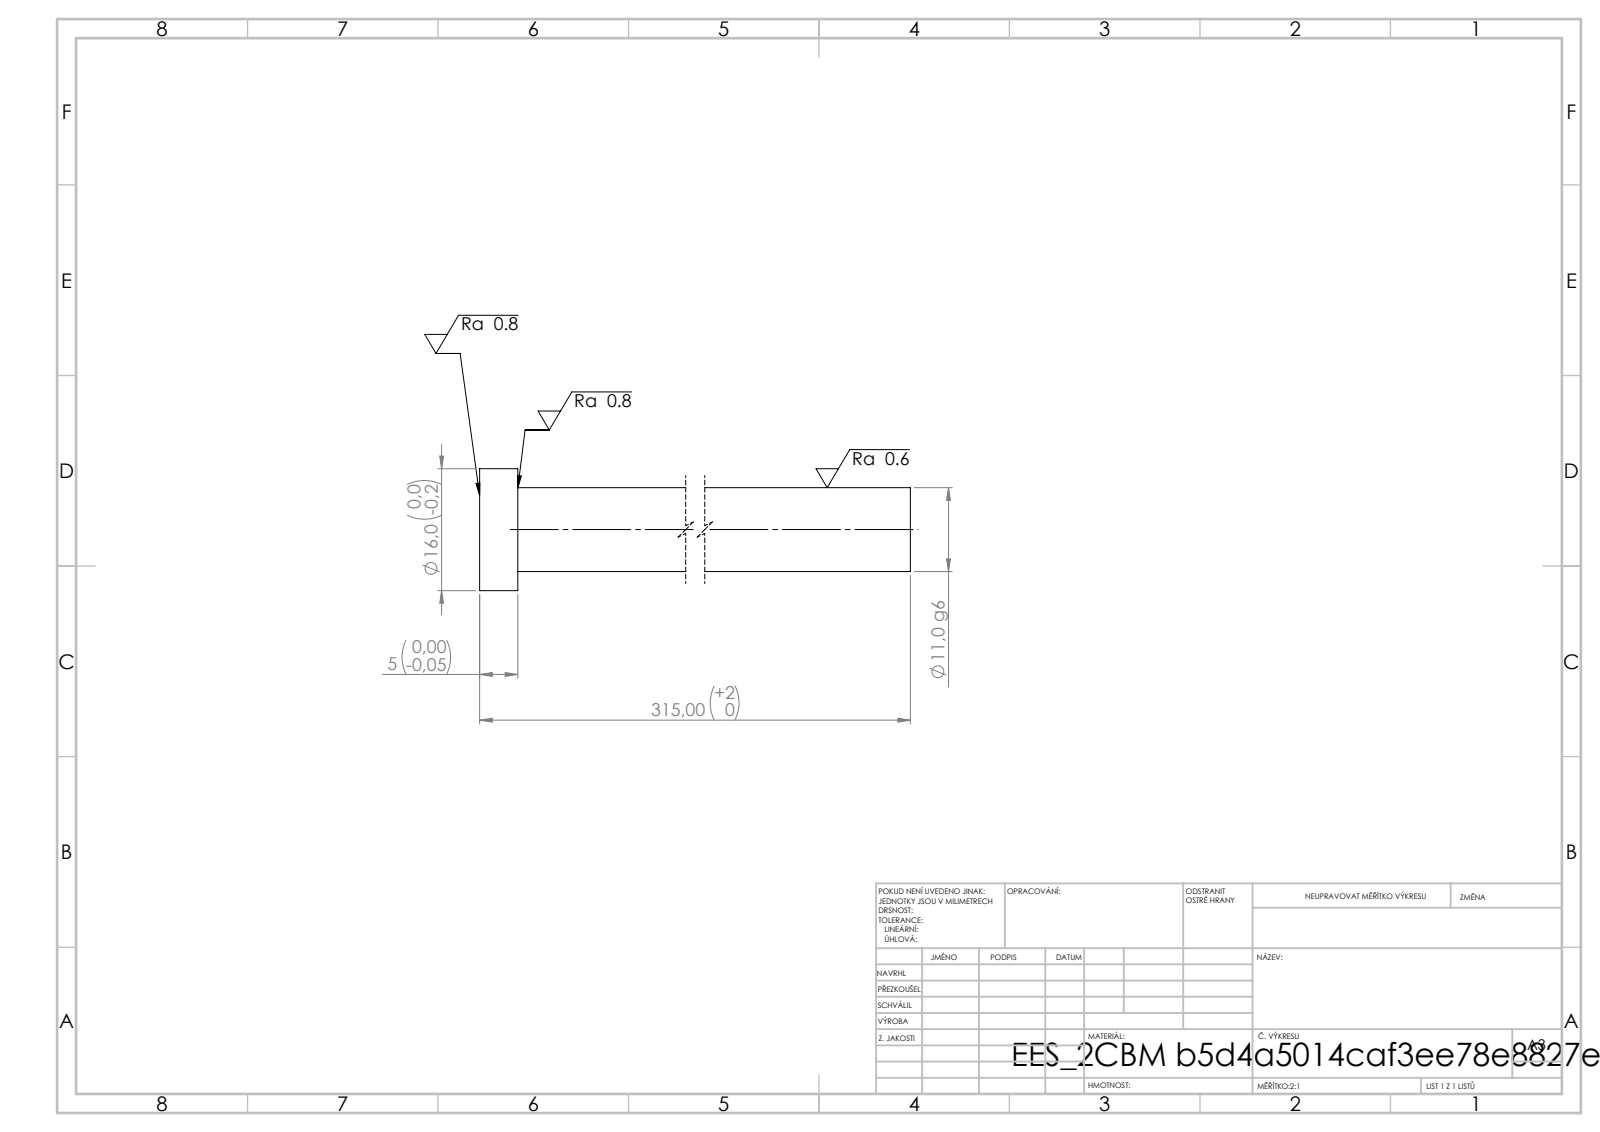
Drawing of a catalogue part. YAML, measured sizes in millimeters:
step_written_by: "SolidWorks 2019 (CONFIG_CONTROL_DESIGN)"
units: millimeters
bodies: {solids: 1, faces: 7, planar: 3, cylindrical: 4, other: 0}
overall_size: [315, 16, 16]
volume: 30466
surface_area: 11366
round_bosses_or_shafts:
  - {diameter: 16, count: 1}
  - {diameter: 11, count: 1}
face_to_face_distances: [5, 315, 310]
